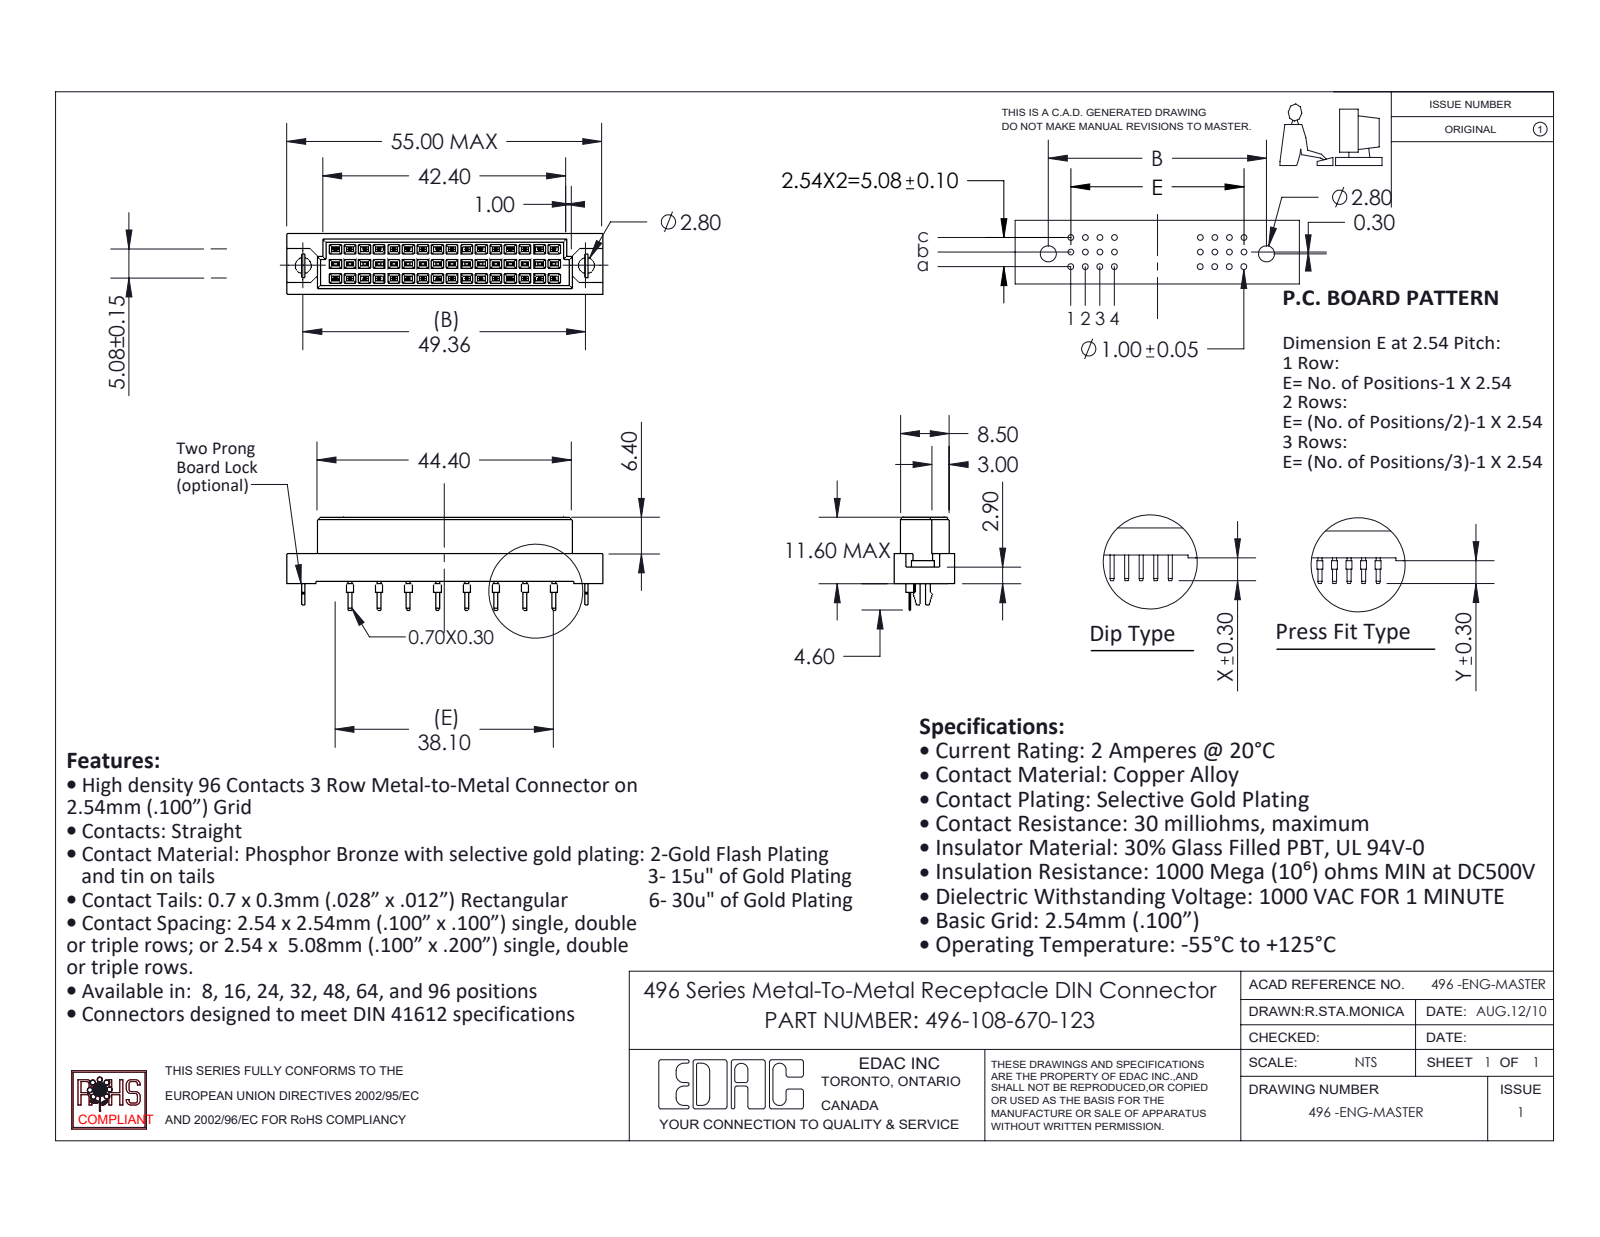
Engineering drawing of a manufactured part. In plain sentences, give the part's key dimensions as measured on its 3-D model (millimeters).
The part is named "496-108-670-123; 496-290_70; 496 Bore-lock; 496 Part_48". Its 3-D file was written by "SolidWorks 2020 (CONFIG_CONTROL_DESIGN)". It is 11 solids with 846 faces: 824 planar, 22 cylindrical and 0 other. Overall it measures 55 by 16.2 by 10.6 millimeters. Its volume is 4 635 cubic millimeters and its surface area 4 503 square millimeters. Round holes: 2 of diameter 2.8. Round bosses or shafts: 8 of diameter 1. Partial cylindrical surfaces (rounded edges, fillets, slot ends): 1 of radius 0.53. The main face-to-face distances are 2.54, 1.05, 9.55, 5.08, 0.81, 10.6, 3.35, 1.73, 8.5, 0.56. The hole center spacings are 49.36.
